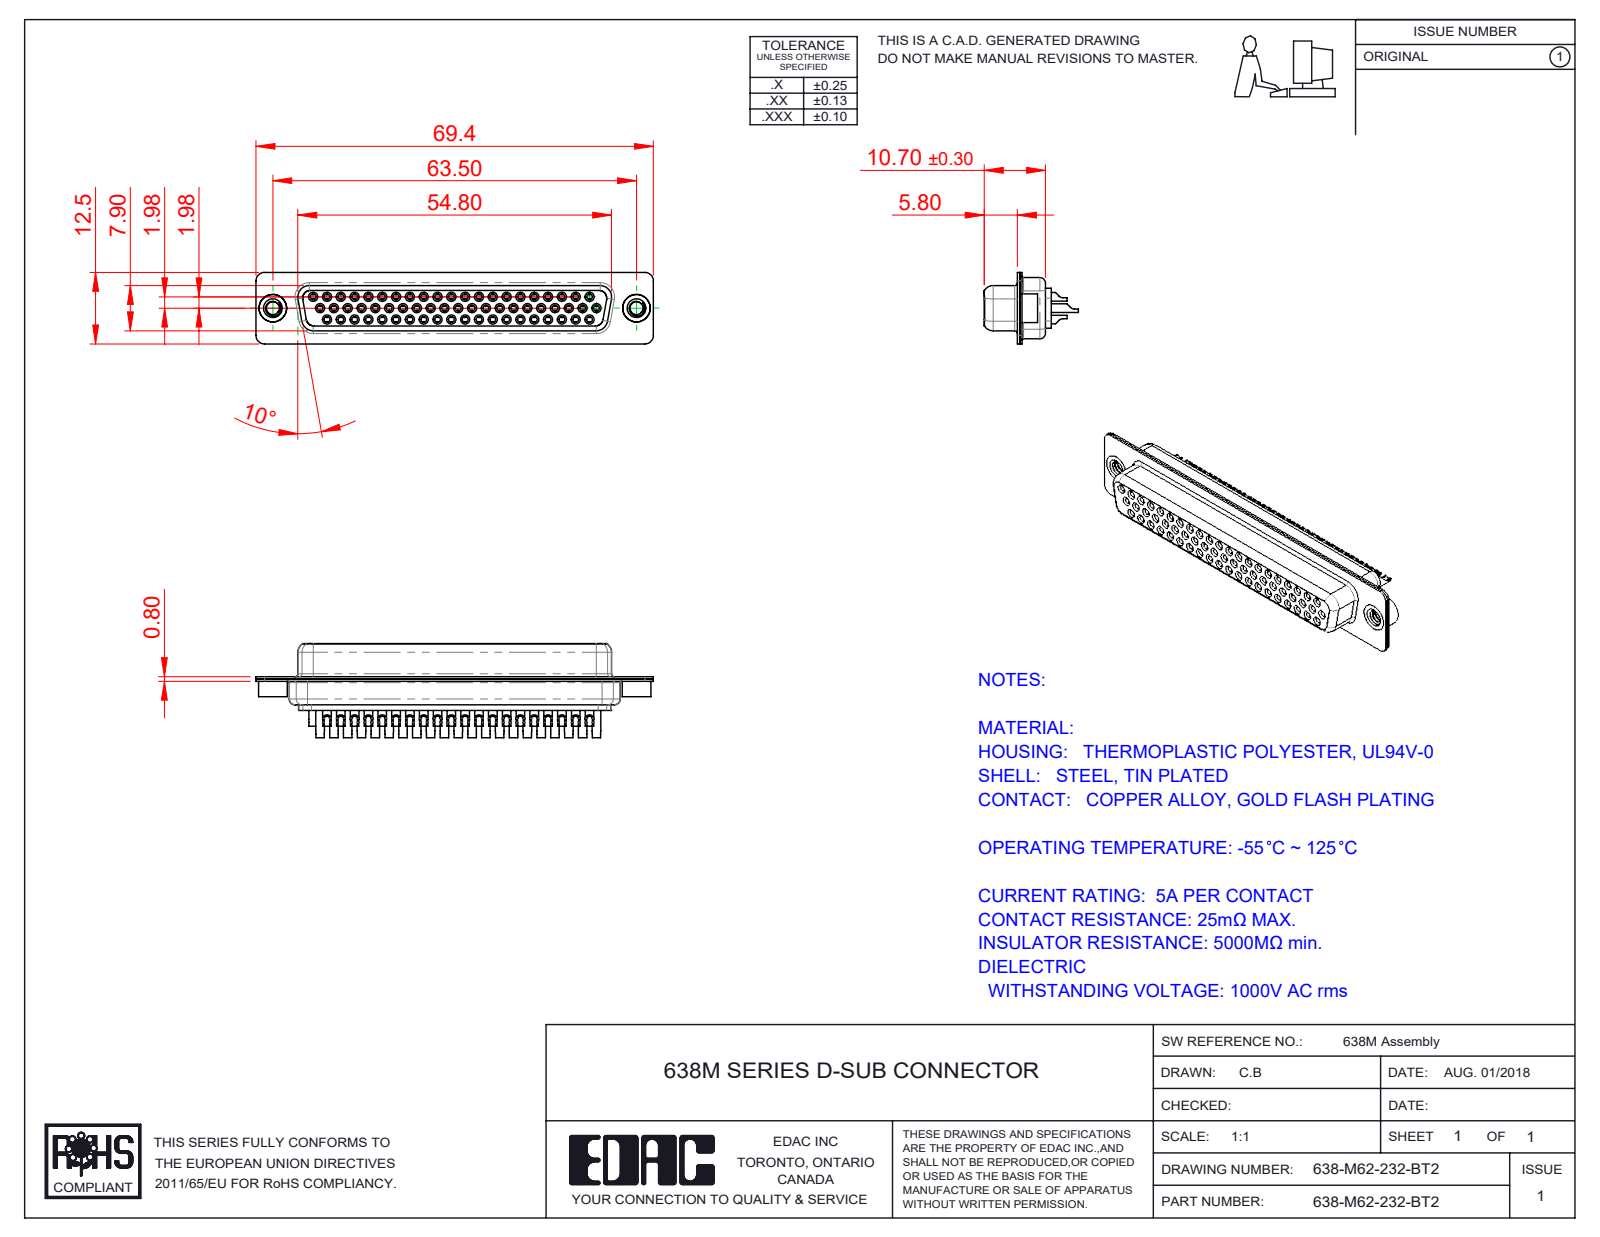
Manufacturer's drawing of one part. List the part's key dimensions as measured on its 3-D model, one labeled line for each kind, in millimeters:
Part name (STEP PRODUCT): 638M Housing_62 Contacts; 638M Contact Row 3_32; 638M Shell Rear_62 Contacts; 638M Contact Row 2_32 (+4 more)
STEP written by: SolidWorks 2020 (CONFIG_CONTROL_DESIGN)
Units: millimetres
Bodies: 67 solids, 3689 faces (1121 planar, 1439 cylindrical, 1129 other)
Overall size (bounding box): 69.4 × 16.45 × 12.5
Volume: 5 074 mm³ · Surface area: 16 874 mm²
Round holes (diameter × count): ⌀1 ×62, ⌀1.1 ×62, ⌀1.7 ×62, ⌀1.8 ×62, ⌀2 ×62, ⌀2.26 ×2, ⌀4 ×2, ⌀4.8 ×2
Round bosses / shafts (diameter × count): ⌀2.2 ×62, ⌀1.6 ×62, ⌀1.5 ×62, ⌀5 ×2, ⌀4.9 ×2
Partial cylindrical surfaces — rounded edges, fillets, slot ends (radius × count): R1.5 ×16, R2 ×12, R1.35 ×8, R1.6 ×8, R1 ×7, R0.25 ×4, R0.5 ×4, R0.6 ×4
Main face-to-face distances: 0.4, 1.4, 0.45, 8.45, 8.9, 1, 1.8, 6.2, 7.05, 1.85
Hole centre spacings: 7.24, 2.32, 2.41, 4.13, 9.65, 4.83, 14.48, 16.89
